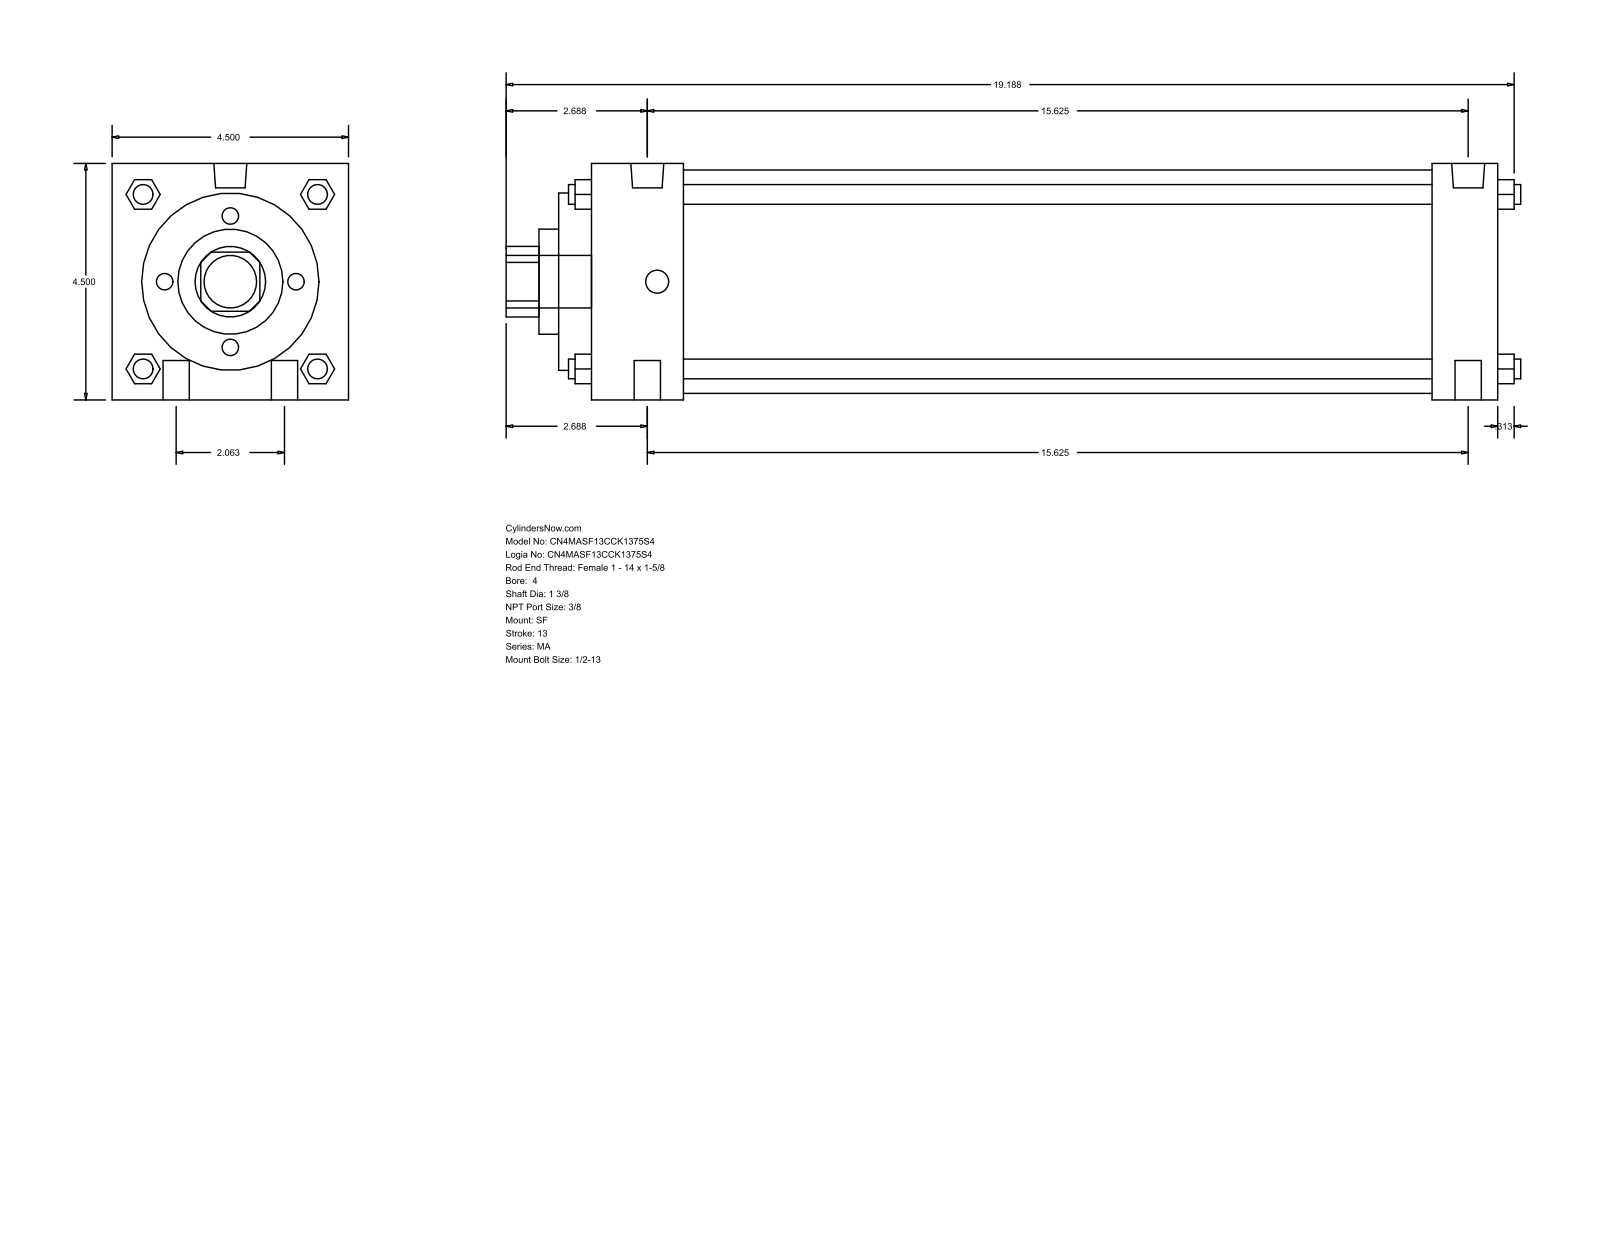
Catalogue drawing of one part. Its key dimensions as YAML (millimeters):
part_name: "MA_SF__0400_1.375"
step_written_by: "GSSL Pune (CONFIG_CONTROL_DESIGN)"
units: millimeters
bodies: {solids: 0, faces: 126, planar: 95, cylindrical: 31, other: 0}
overall_size: [490.54, 114.3, 114.3]
round_holes:
  - {diameter: 34.92, count: 1}
  - {diameter: 50.8, count: 1}
  - {diameter: 85.72, count: 1}
  - {diameter: 107.95, count: 1}
round_bosses_or_shafts:
  - {diameter: 12.7, count: 4}
  - {diameter: 9.53, count: 4}
  - {diameter: 15.93, count: 2}
  - {diameter: 11.11, count: 2}
  - {diameter: 25.4, count: 1}
partial_cylinders:
  - {radius: 17.06, count: 1}
face_to_face_distances: [114.3, 438.16, 15.87, 454.03, 422.28, 406.41, 31.75, 60.32, 44.45, 361.96]
